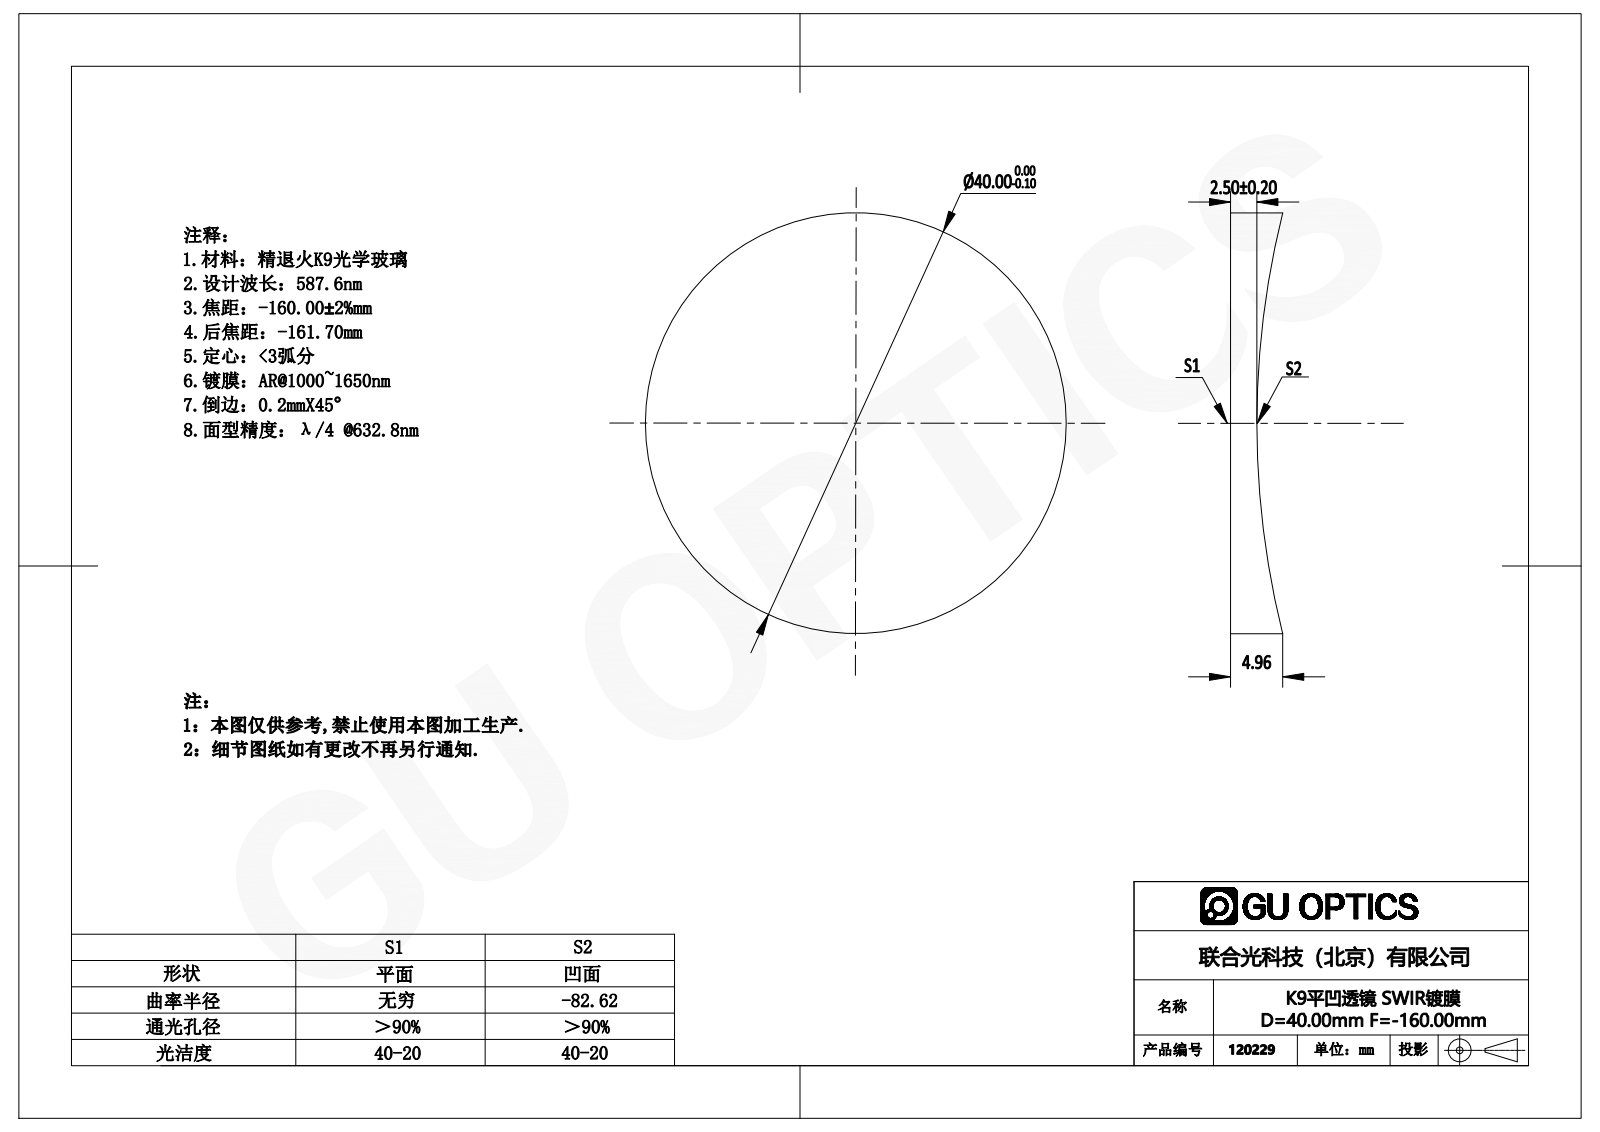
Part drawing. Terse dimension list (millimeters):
name: 120169
written by: SolidWorks 2016 (AUTOMOTIVE_DESIGN)
unit: mm
bodies: 1 solid, 5 faces (1 planar, 2 cylindrical, 2 other)
size: 40 × 40 × 4.96
volume: 4 679 mm³; area: 3 155 mm²
bosses: 1× ⌀40
